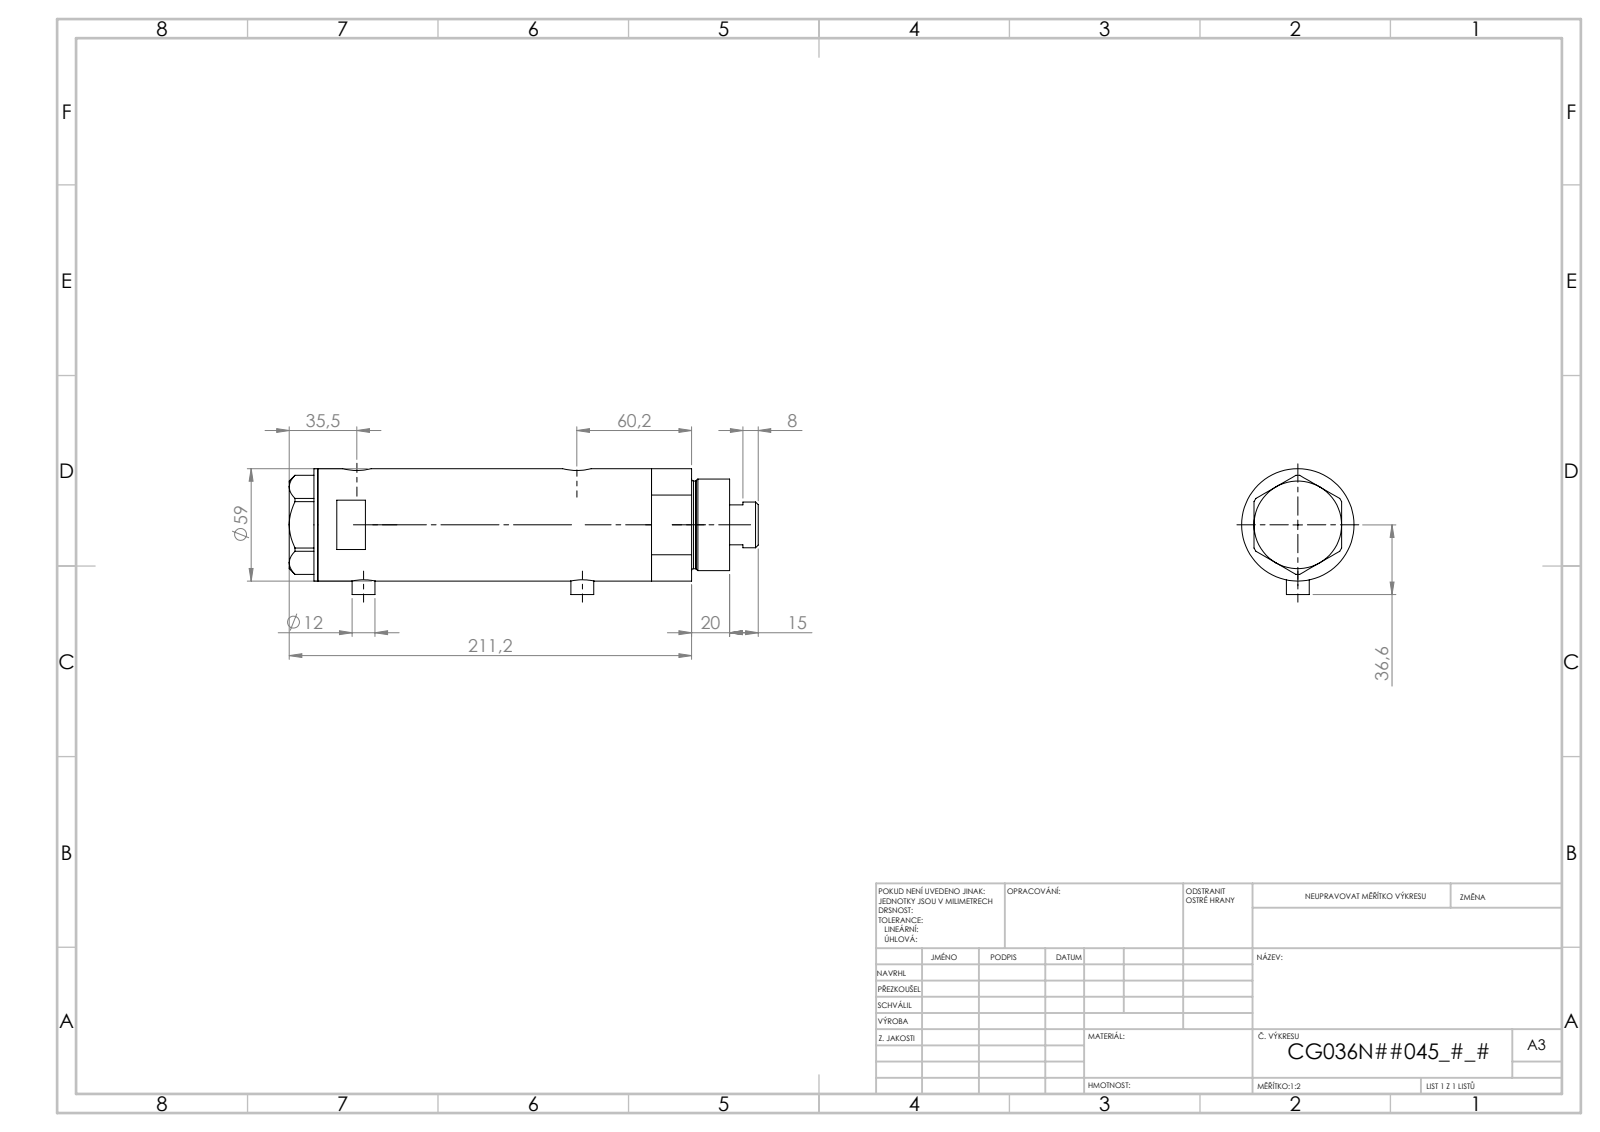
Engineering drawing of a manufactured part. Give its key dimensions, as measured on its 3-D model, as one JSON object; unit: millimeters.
{"part_name": "V270CG_FRONT; V270CG_BACK; V270CG_VC; V270CG_MIDDLE", "step_written_by": "SolidWorks 2019 (CONFIG_CONTROL_DESIGN)", "units": "millimeters", "bodies": {"solids": 4, "faces": 126, "planar": 53, "cylindrical": 53, "other": 20}, "overall_size": [208.42, 60.1, 59], "volume_mm3": 470455, "surface_area_mm2": 98858, "round_holes": [[5, 2], [9.73, 2], [12.5, 2], [15, 2], [8.5, 1], [25, 1], [26.5, 1], [36, 1], [40, 1], [52, 1]], "round_bosses_or_shafts": [[12, 2], [59, 1], [48, 1], [46, 1], [24, 1]], "face_to_face_distances": [78.85, 15, 117.34, 102.34, 193.42, 38.5, 23.5, 78.84, 38.49, 23.49], "hole_center_spacings": [2.9, 3.5, 77.15, 80.05, 80.65, 83.55, 2.89, 2.91]}
